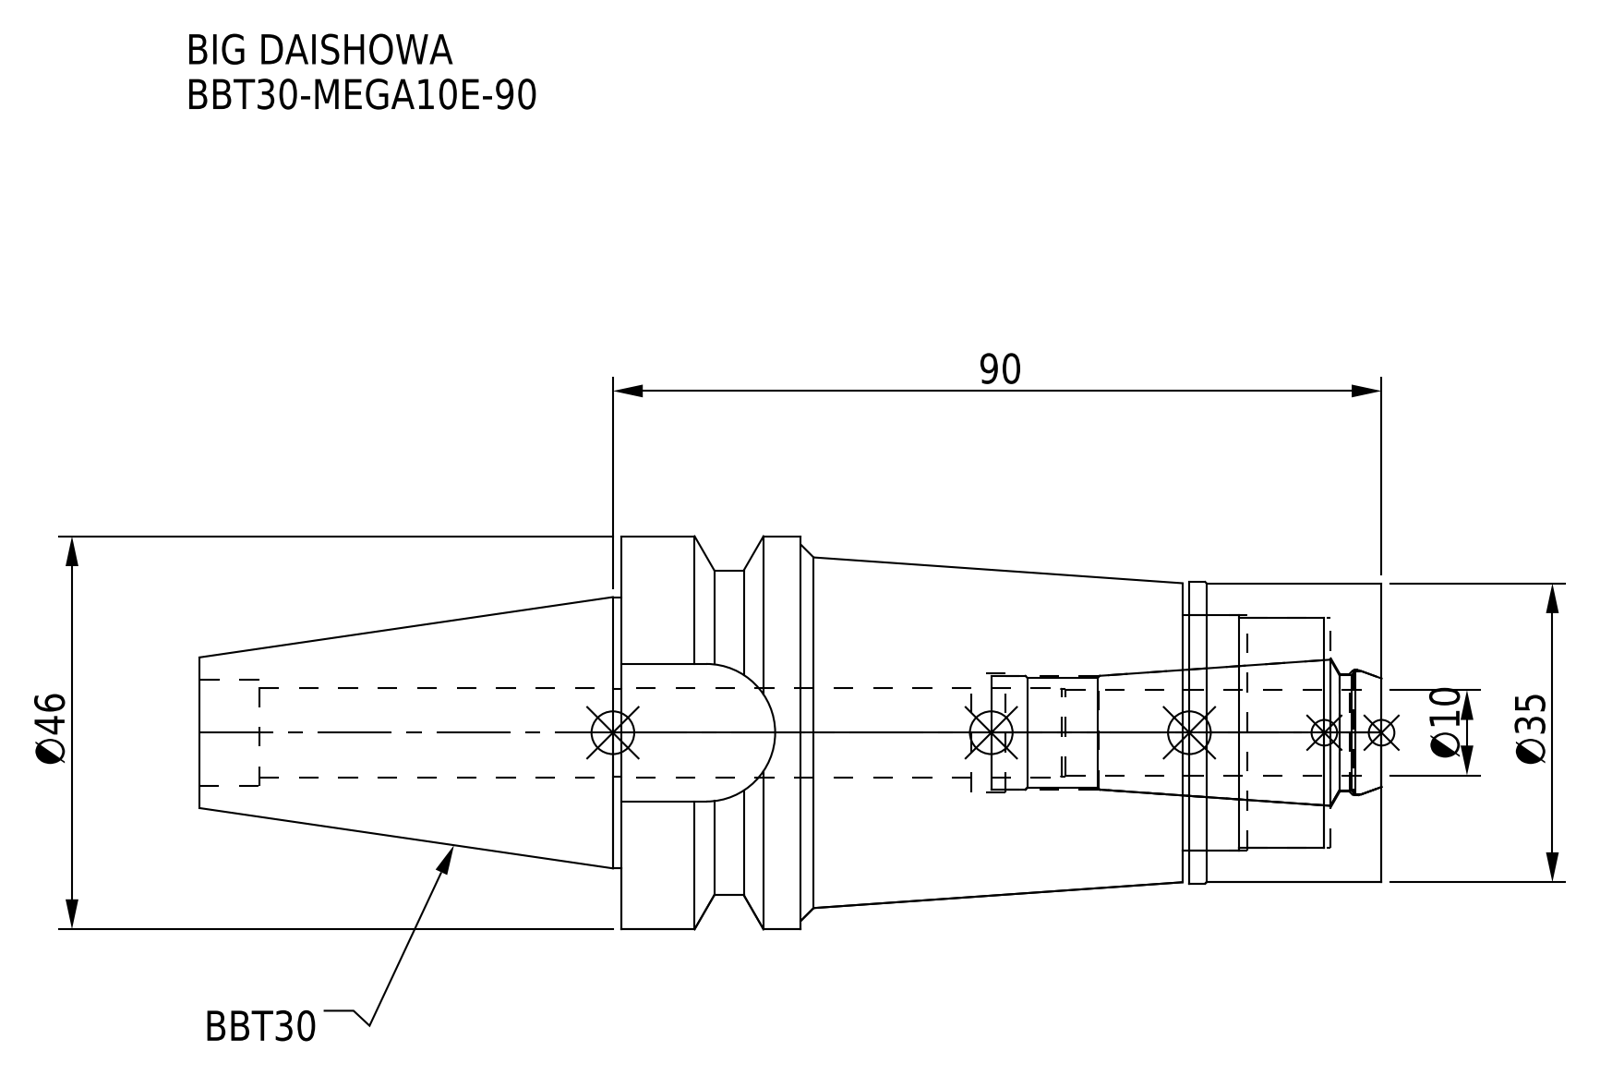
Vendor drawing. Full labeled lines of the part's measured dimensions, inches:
Part name (STEP PRODUCT): MEN10_1.stp; BBT30-MEGA10E-90-100.stp; DXF_TEMP_ASSY_ASM_4_ASM.stp; BBT30-MEGA10E-90-100-FreeParts (+3 more)
STEP written by: SolidWorks 2019 (CONFIG_CONTROL_DESIGN)
Units: inches
Bodies: 2 solids, 79 faces (21 planar, 38 cylindrical, 20 other)
Overall size (bounding box): 5.449 × 1.811 × 1.811
Volume: 6.776 in³ · Surface area: 41.86 in²
Round holes (diameter × count): ⌀0.402 ×1, ⌀0.409 ×1, ⌀0.492 ×1, ⌀0.524 ×1, ⌀0.543 ×1, ⌀0.547 ×1, ⌀0.579 ×1, ⌀1.063 ×1, ⌀1.083 ×1
Round bosses / shafts (diameter × count): ⌀1.811 ×1, ⌀1.39 ×1, ⌀1.378 ×1, ⌀1.25 ×1
Partial cylindrical surfaces — rounded edges, fillets, slot ends (radius × count): R0.317 ×1, R0.748 ×1
Main face-to-face distances: 3.504, 0.886, 2.618, 0.917, 0.031, 2.587, 0.264, 0.622, 0.654, 3.24
